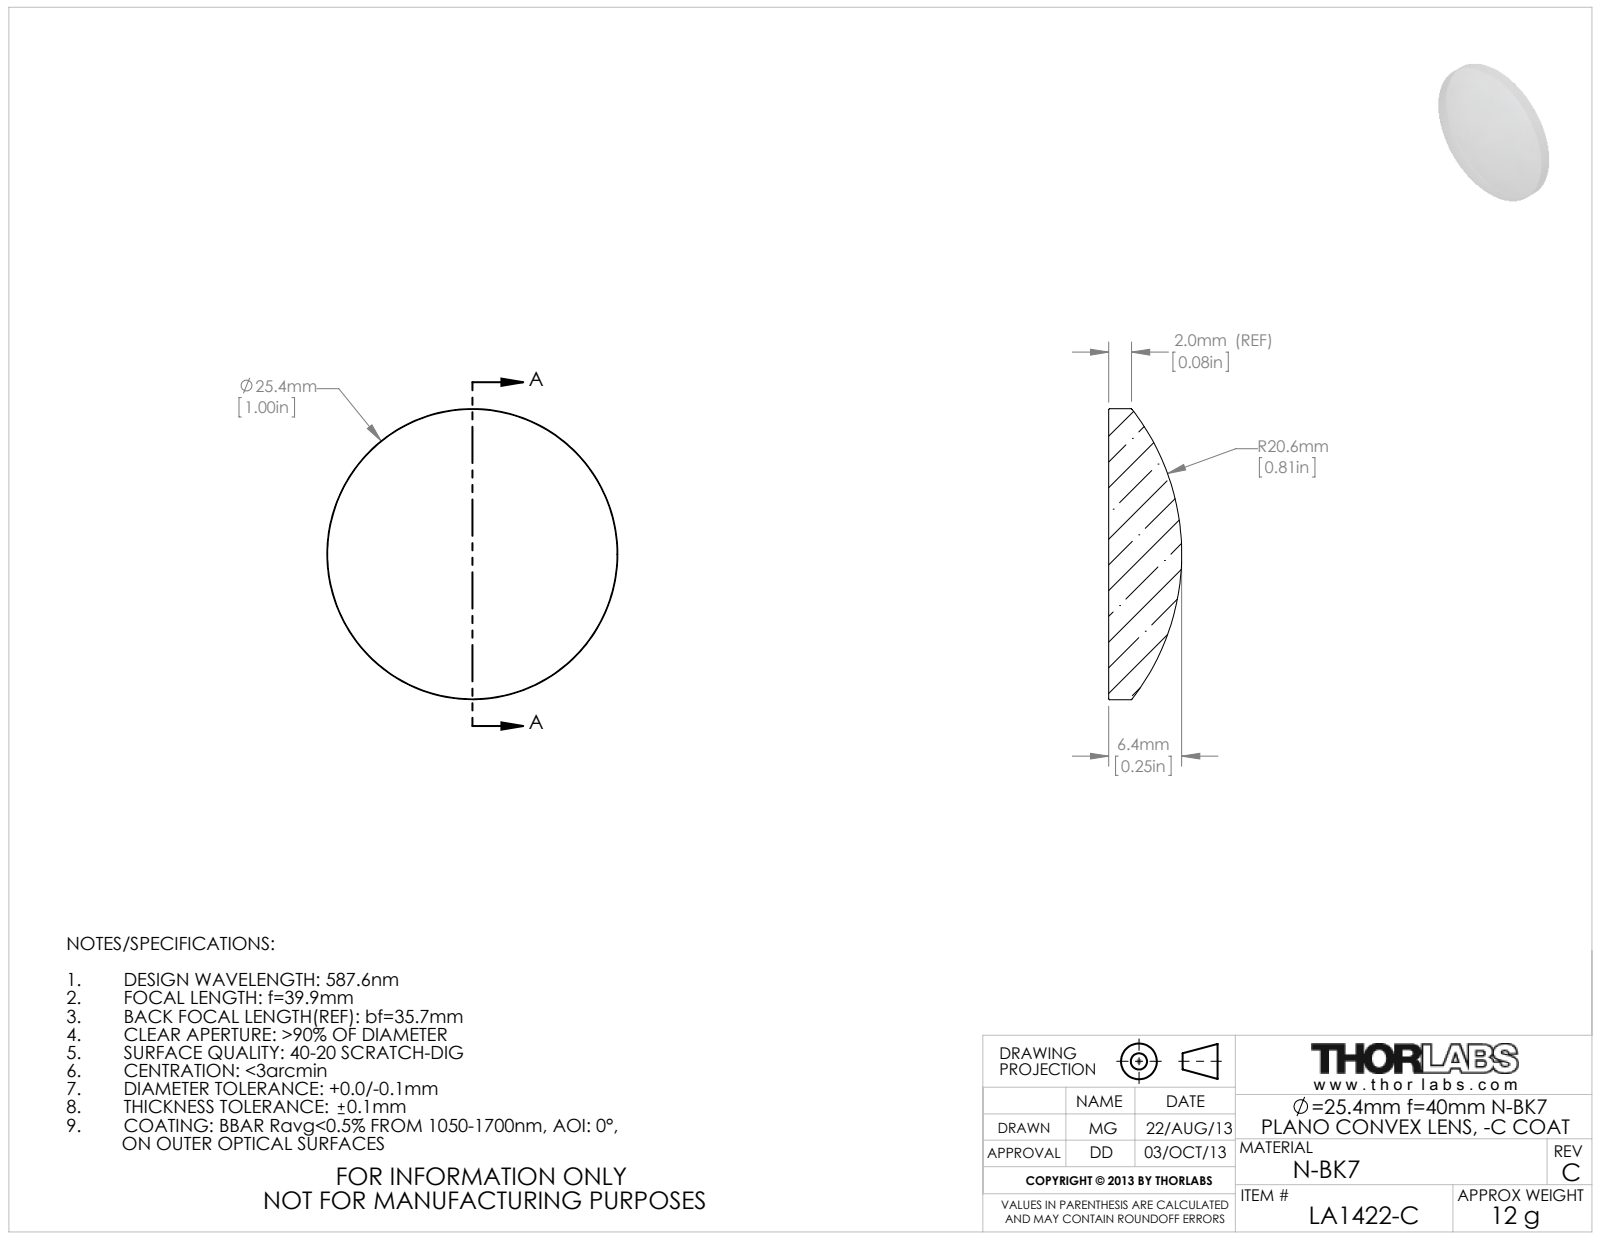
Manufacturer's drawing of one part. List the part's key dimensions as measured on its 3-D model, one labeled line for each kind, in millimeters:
Part name (STEP PRODUCT): 4580-E0W
STEP written by: SolidWorks 2009 (AUTOMOTIVE_DESIGN)
Units: millimetres
Bodies: 1 solid, 5 faces (1 planar, 2 cylindrical, 2 other)
Overall size (bounding box): 25.4 × 25.4 × 6.37
Volume: 2 162 mm³ · Surface area: 1 232 mm²
Round bosses / shafts (diameter × count): ⌀25.4 ×1
